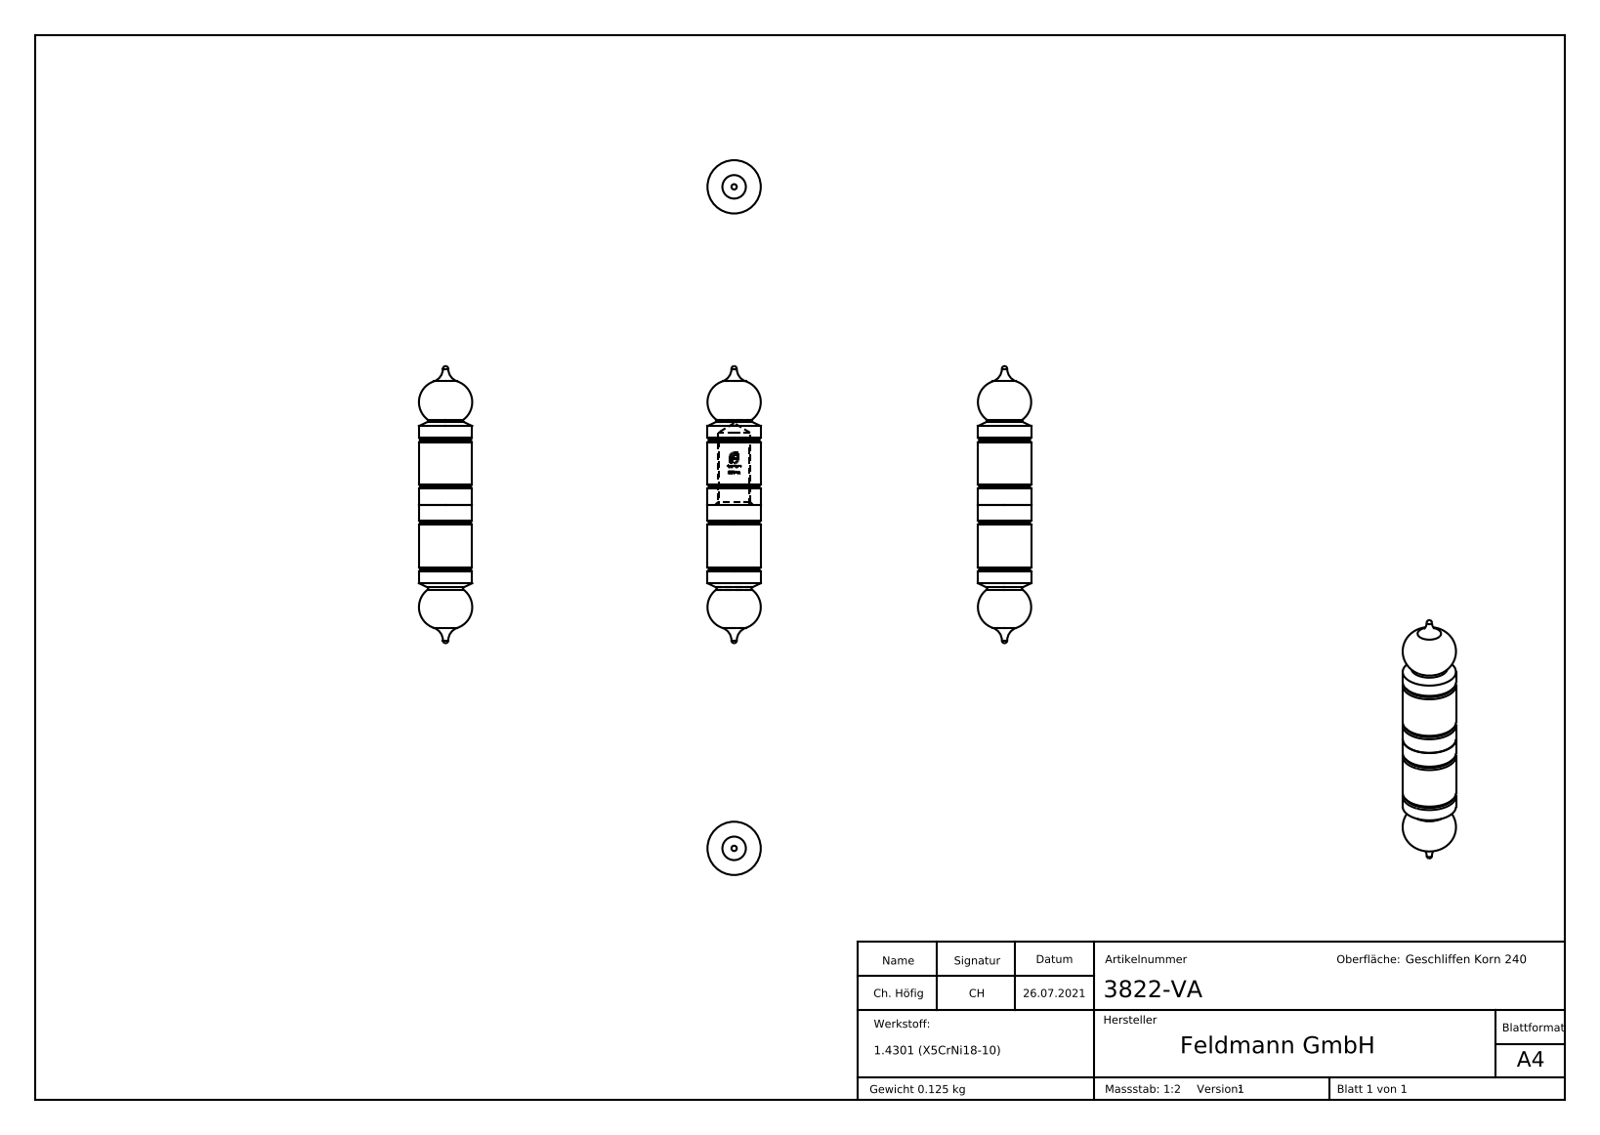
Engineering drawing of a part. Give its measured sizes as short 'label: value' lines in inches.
name: 382X-VA Teil1; 3822-VA; 382X-VA Teil1_3822-VA Teil2; 382X-VA Teil1_3822-VA Teil1
written by: SolidWorks 2018 (CONFIG_CONTROL_DESIGN)
unit: in
bodies: 2 solids, 282 faces (116 planar, 34 cylindrical, 132 other)
size: 4.094 × 0.787 × 0.787
volume: 1.578 in³; area: 13.74 in²
holes: 1× ⌀0.472
bosses: 1× ⌀0.787, 1× ⌀0.748, 1× ⌀0.453
rounds: 1× R0.24
face distances: 0.984, 0.012, 0.017, 0.013, 0.081, 0.123, 0.098, 0.217, 0.034, 0.076
